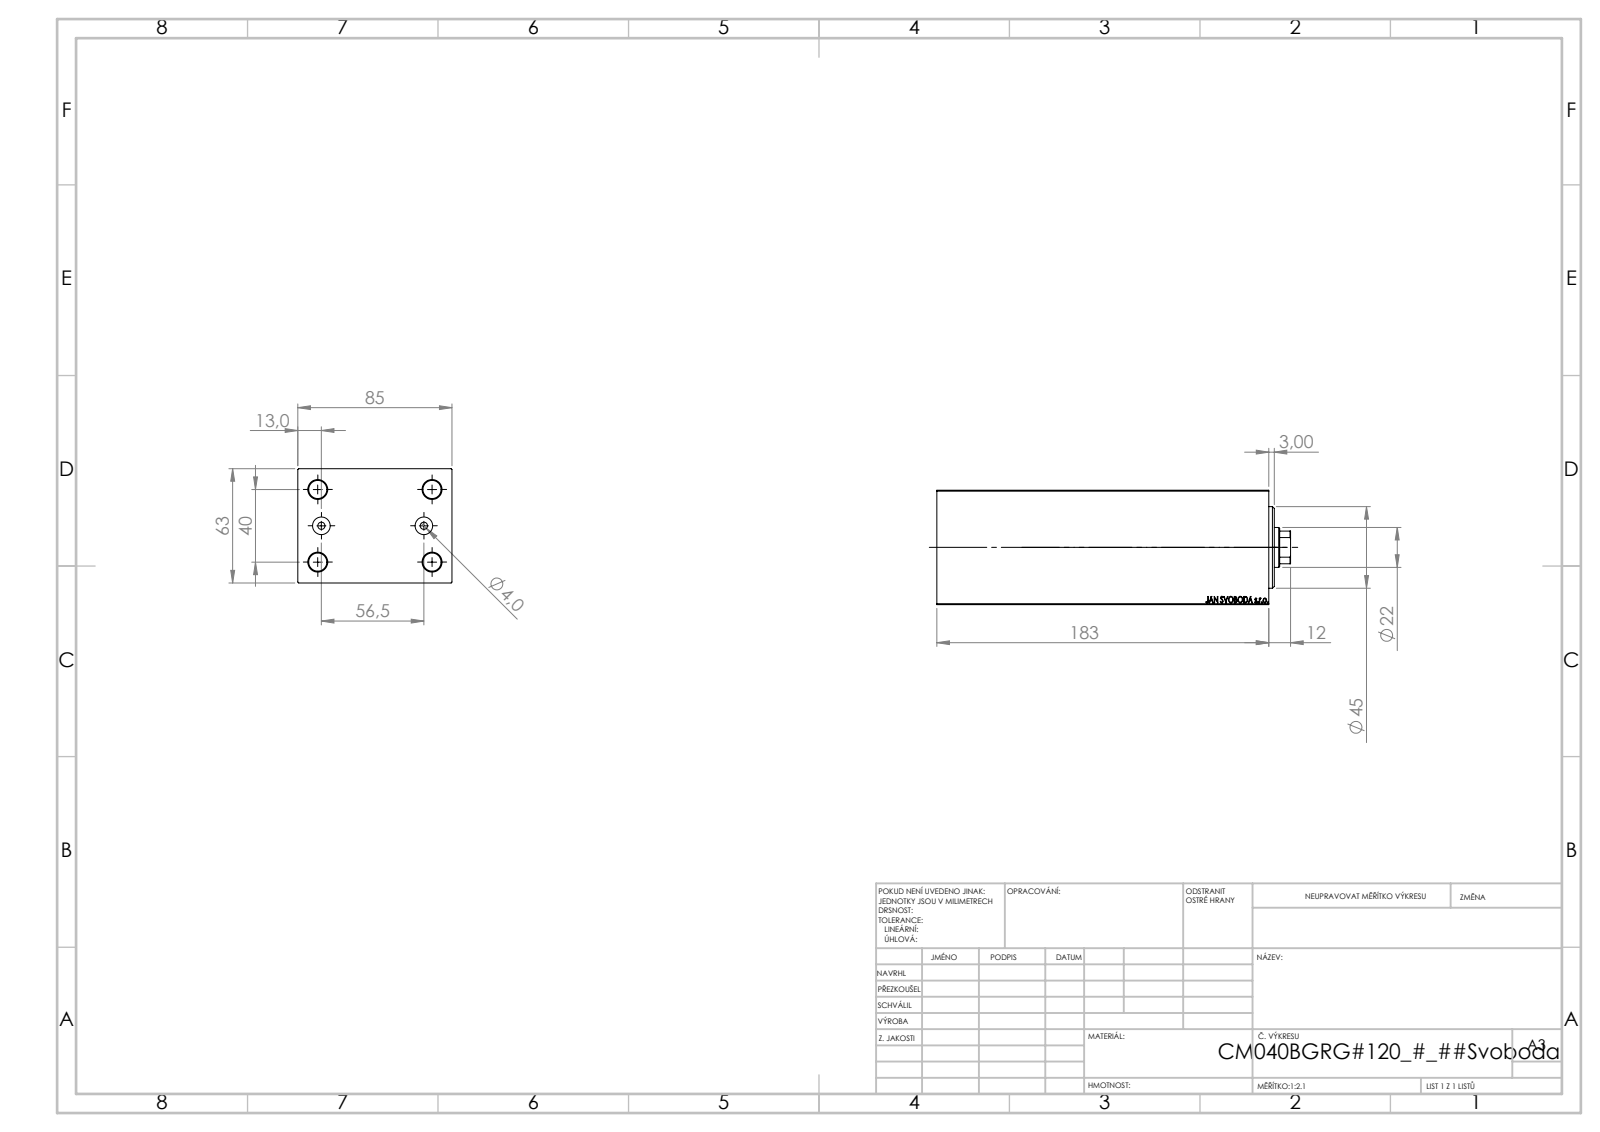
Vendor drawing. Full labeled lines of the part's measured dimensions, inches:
Part name (STEP PRODUCT): V450CM_B_Body; V450CM_B_VCP; V450CM_VC_B
STEP written by: SolidWorks 2019 (CONFIG_CONTROL_DESIGN)
Units: inches
Bodies: 3 solids, 877 faces (401 planar, 50 cylindrical, 426 other)
Overall size (bounding box): 7.677 × 3.346 × 2.48
Volume: 52.52 in³ · Surface area: 185.6 in²
Round holes (diameter × count): ⌀0.394 ×4, ⌀0.157 ×2, ⌀0.383 ×2, ⌀0.492 ×1, ⌀0.866 ×1, ⌀1.004 ×1, ⌀1.043 ×1, ⌀1.575 ×1, ⌀1.654 ×1, ⌀1.772 ×1
Partial cylindrical surfaces — rounded edges, fillets, slot ends (radius × count): R0.413 ×1
Main face-to-face distances: 2.48, 3.346, 0.472, 6.732, 7.205, 6.26, 0.118, 0.591, 6.85, 7.323
Hole centre spacings: 1.469, 0.791, 0.807, 1.575, 2.434, 2.48, 2.528, 2.938
